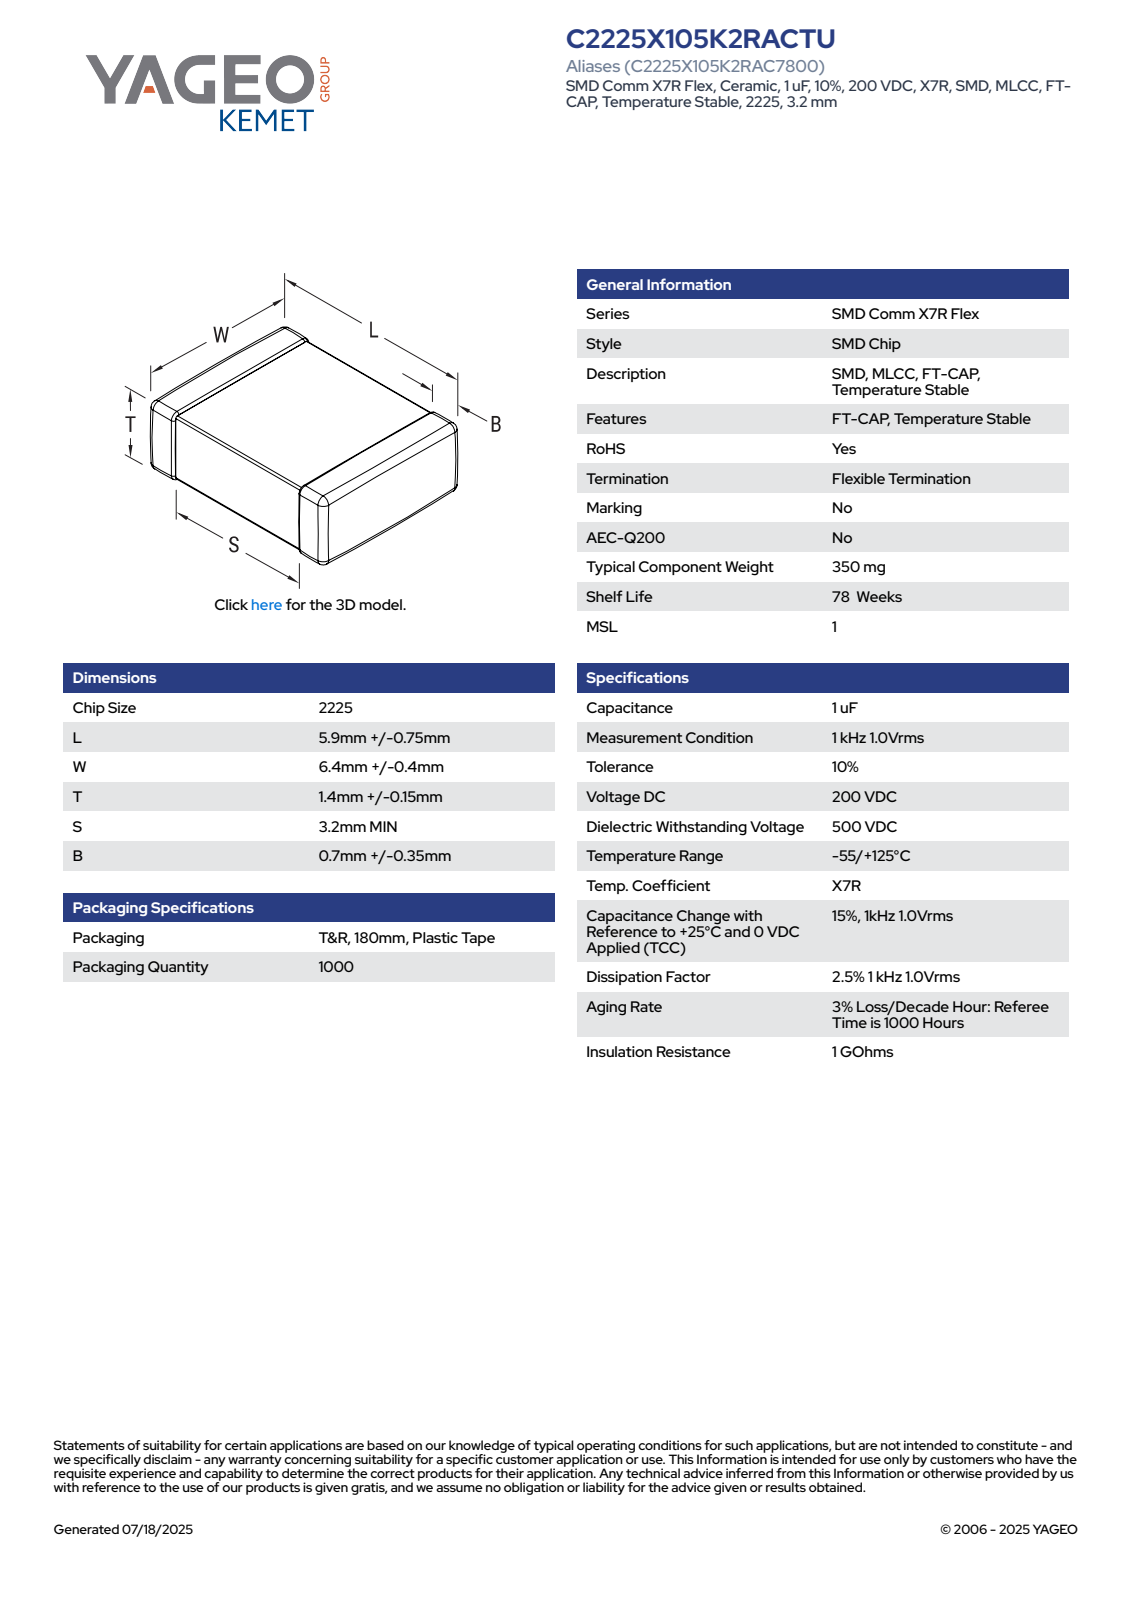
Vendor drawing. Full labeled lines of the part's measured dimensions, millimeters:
Part name (STEP PRODUCT): CCS_CCSTDNOS_2225_L6.65W6.8T1.55B1.05
STEP written by: SolidWorks 2014 (AUTOMOTIVE_DESIGN)
Units: millimetres
Bodies: 4 solids, 125 faces (71 planar, 38 cylindrical, 16 other)
Overall size (bounding box): 6.8 × 6.65 × 1.55
Volume: 59 mm³ · Surface area: 127 mm²
Partial cylindrical surfaces — rounded edges, fillets, slot ends (radius × count): R0.14 ×24
Main face-to-face distances: 1.27, 1.41, 1.55, 6.65, 6.52, 6.66, 6.8, 3.29, 3.37, 0.47
